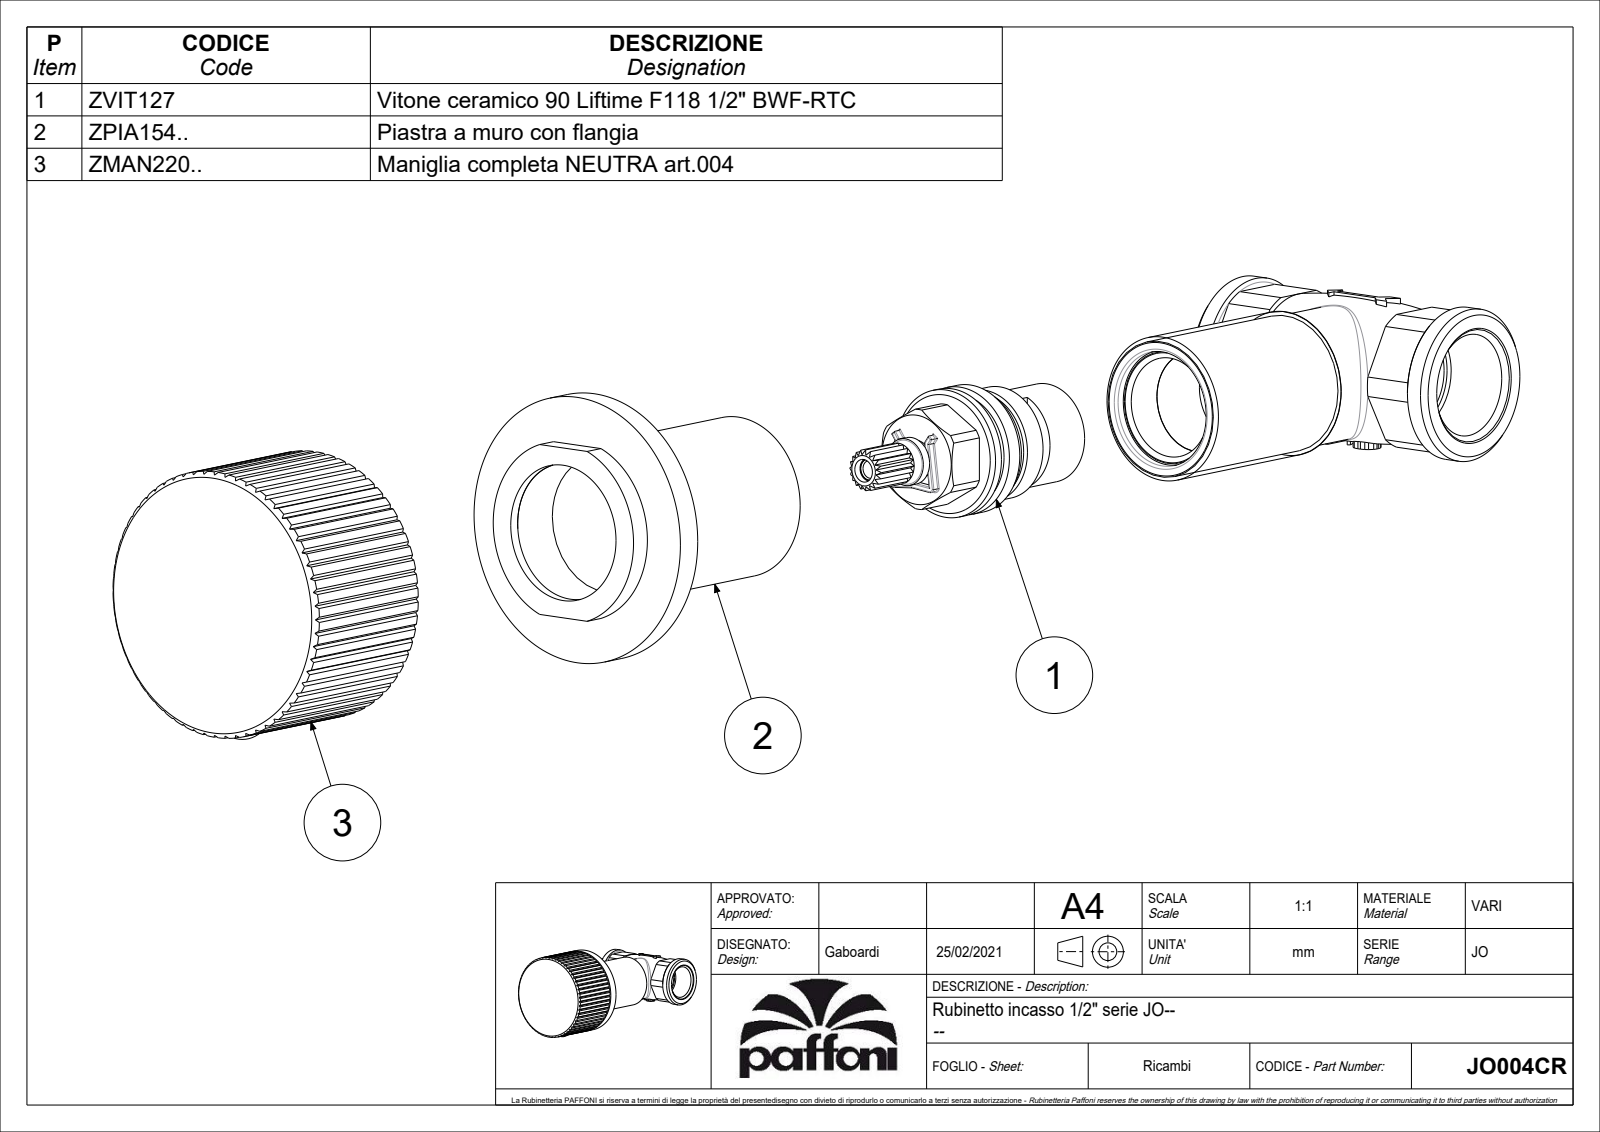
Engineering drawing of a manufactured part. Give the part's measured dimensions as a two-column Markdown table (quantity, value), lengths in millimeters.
| quantity | value |
| --- | --- |
| part name | JO004CR |
| STEP written by | CREO PARAMETRIC BY PTC INC, 2020044 (CONFIG_CONTROL_DESIGN) |
| units | millimeters |
| bodies | 2 solids, 523 faces (275 planar, 154 cylindrical, 94 other) |
| overall size | 51.3 × 50 × 35.7 |
| volume | 55 739 mm³ |
| surface area | 20 127 mm² |
| round holes (diameter × count) | 4.2 × 1, 8 × 1, 15 × 1, 25.5 × 1, 36 × 1, 46.2 × 1 |
| round bosses / shafts (diameter × count) | 50 × 1, 47 × 1, 41.2 × 1, 30 × 1, 24 × 1, 22 × 1, 21.4 × 1, 8.8 × 1 |
| partial cylindrical surfaces (radius × count) | 0.2 × 26, 0.5 × 12, 1 × 2, 9.4 × 1, 13.4 × 1 |
| main face-to-face distances | 34.66, 34.64, 2, 9, 27.3, 7, 5.7, 4, 3, 5 |
